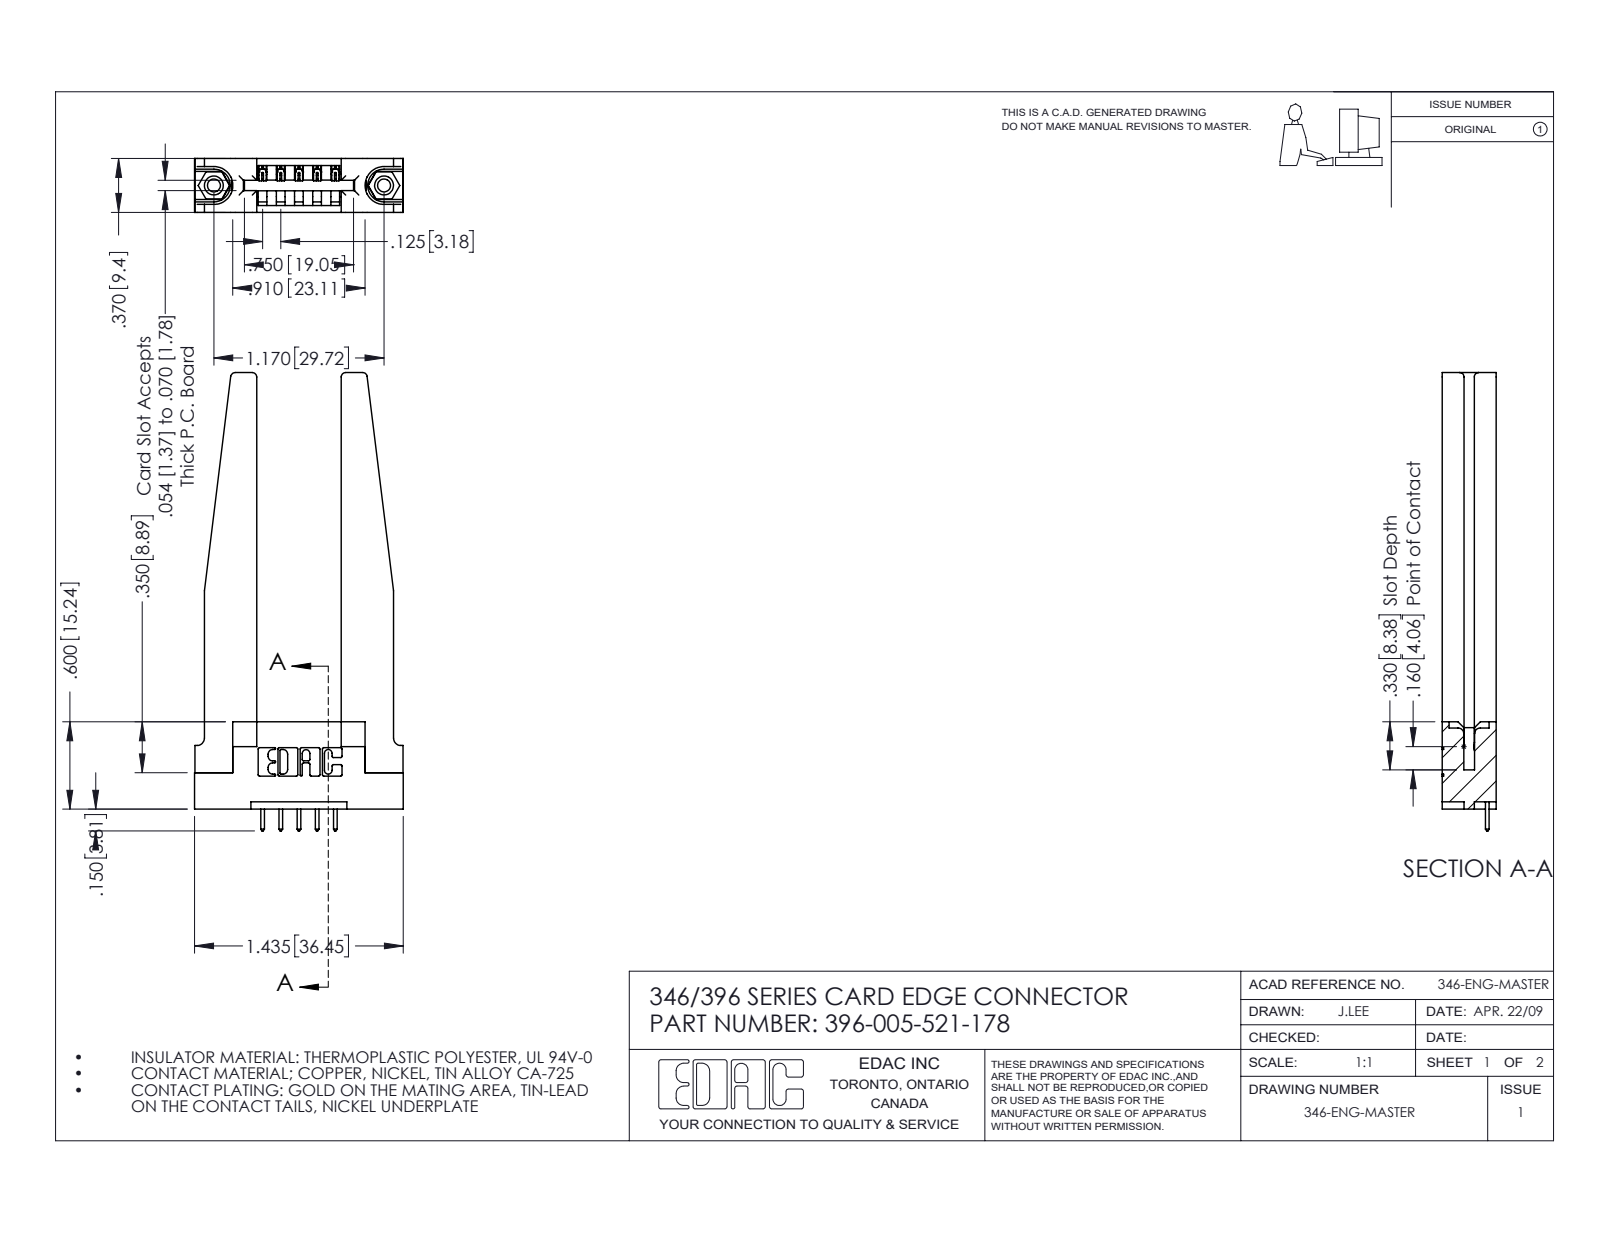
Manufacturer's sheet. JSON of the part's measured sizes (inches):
{"part_name": "346-220-078_345-220-078; 396-005-521-178; 345-292-001_345-293-121; 345-250-001_345-250-001-102 (+1 more)", "step_written_by": "SolidWorks 2016 (CONFIG_CONTROL_DESIGN)", "units": "inches", "bodies": {"solids": 10, "faces": 646, "planar": 418, "cylindrical": 176, "other": 52}, "overall_size": [3.15, 1.435, 0.37], "volume_in3": 0.618, "surface_area_in2": 15.67, "round_holes": [[0.089, 2], [0.125, 2], [0.156, 2], [0.064, 1]], "round_bosses_or_shafts": [[0.155, 2]], "partial_cylinders_radius": [[0.01, 22], [0.006, 10], [0.01, 10], [0.03, 8], [0.007, 6], [0.031, 6], [0.026, 3], [0.031, 2]], "face_to_face_distances": [0.37, 0.15, 0.22, 0.25, 0.581, 0.072, 0.148, 0.071, 0.102, 0.048], "hole_center_spacings": [0.246, 0.969, 1.17]}
